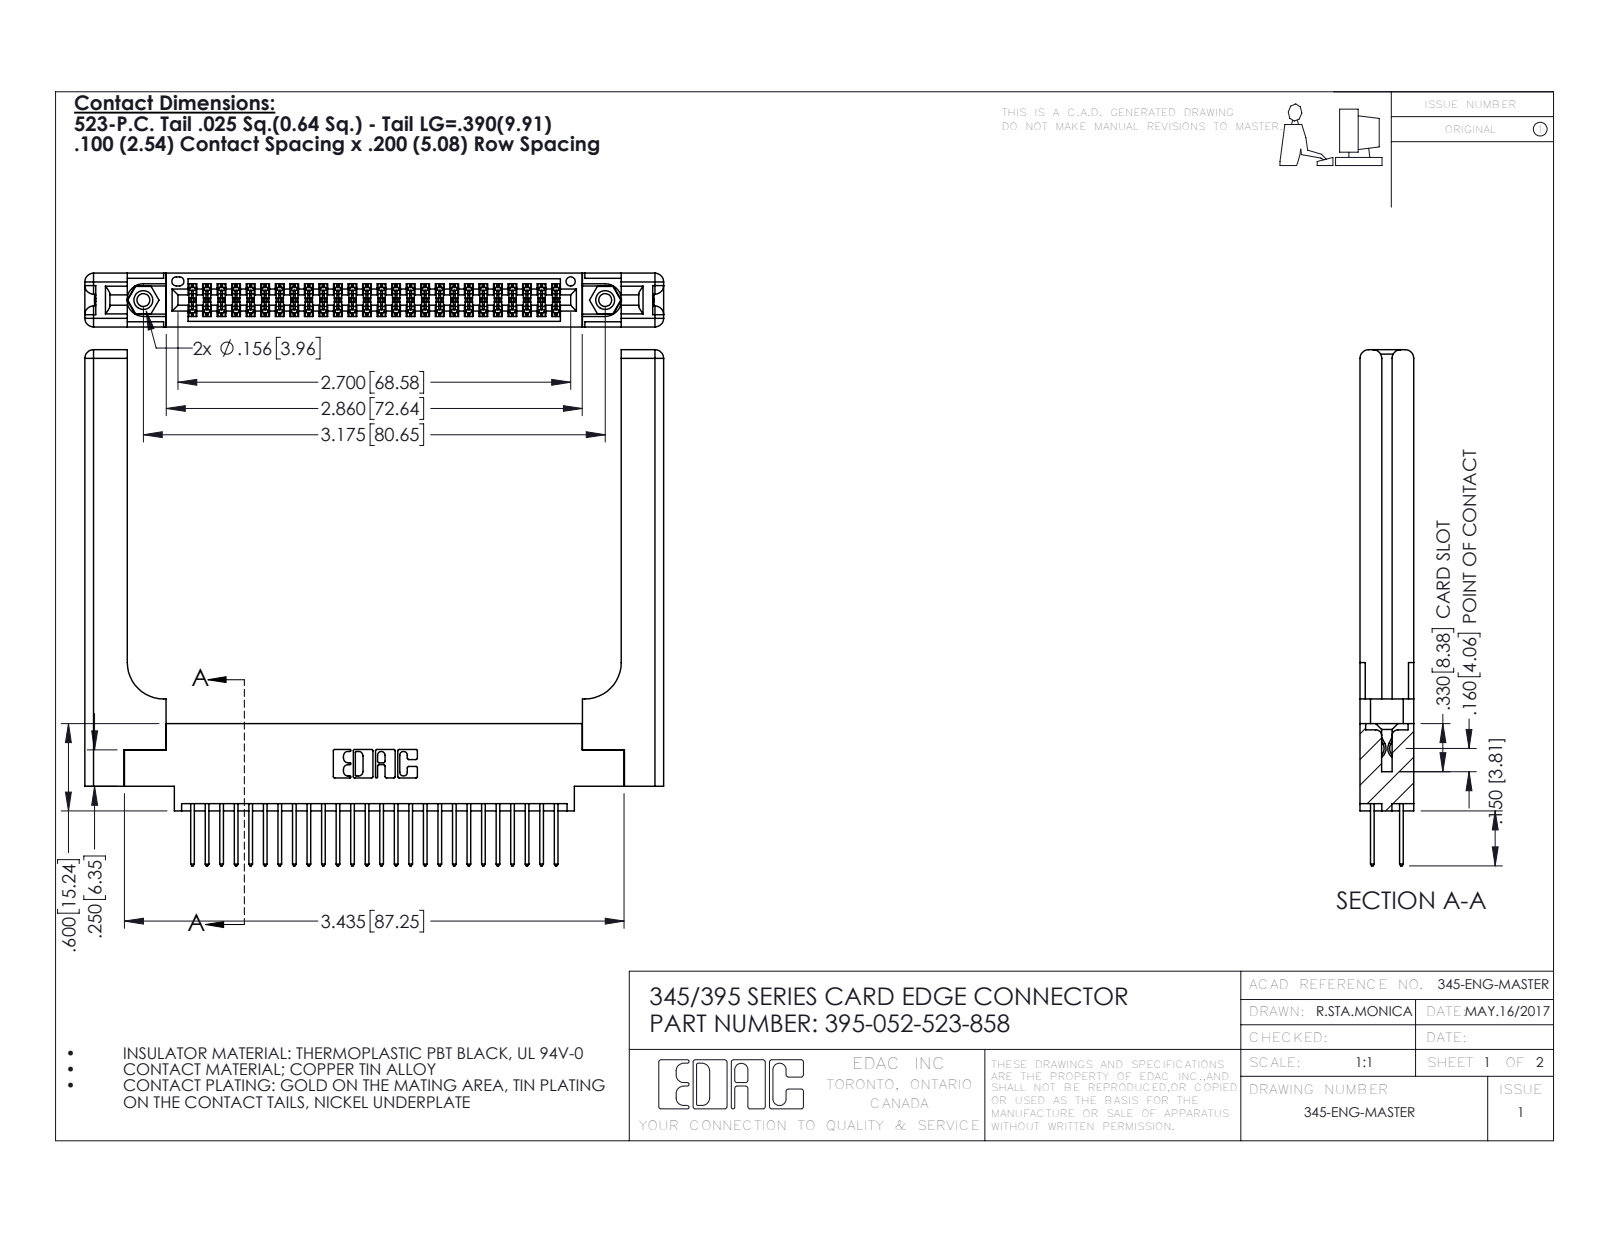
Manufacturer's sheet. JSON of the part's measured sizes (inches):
{"part_name": "345-250-001_345-250-001-102; 345 Part_0.170 Offset - 0.156 Dia-TH; 345-220-058_345-220-058; 395-052-523-858 (+1 more)", "step_written_by": "SolidWorks 2016 (CONFIG_CONTROL_DESIGN)", "units": "inches", "bodies": {"solids": 57, "faces": 2986, "planar": 1948, "cylindrical": 978, "other": 60}, "overall_size": [3.979, 3.547, 0.37], "volume_in3": 1.107, "surface_area_in2": 30.46, "round_holes": [[0.089, 2], [0.125, 2], [0.156, 2], [0.064, 1]], "round_bosses_or_shafts": [[0.155, 2]], "partial_cylinders_radius": [[0.006, 78], [0.01, 52], [0.01, 22], [0.06, 16], [0.007, 6], [0.031, 6], [0.026, 3], [0.014, 2]], "face_to_face_distances": [0.37, 0.072, 0.298, 0.098, 0.272, 0.025, 0.2, 0.225, 0.148, 0.15], "hole_center_spacings": [0.27, 2.94, 3.175]}
